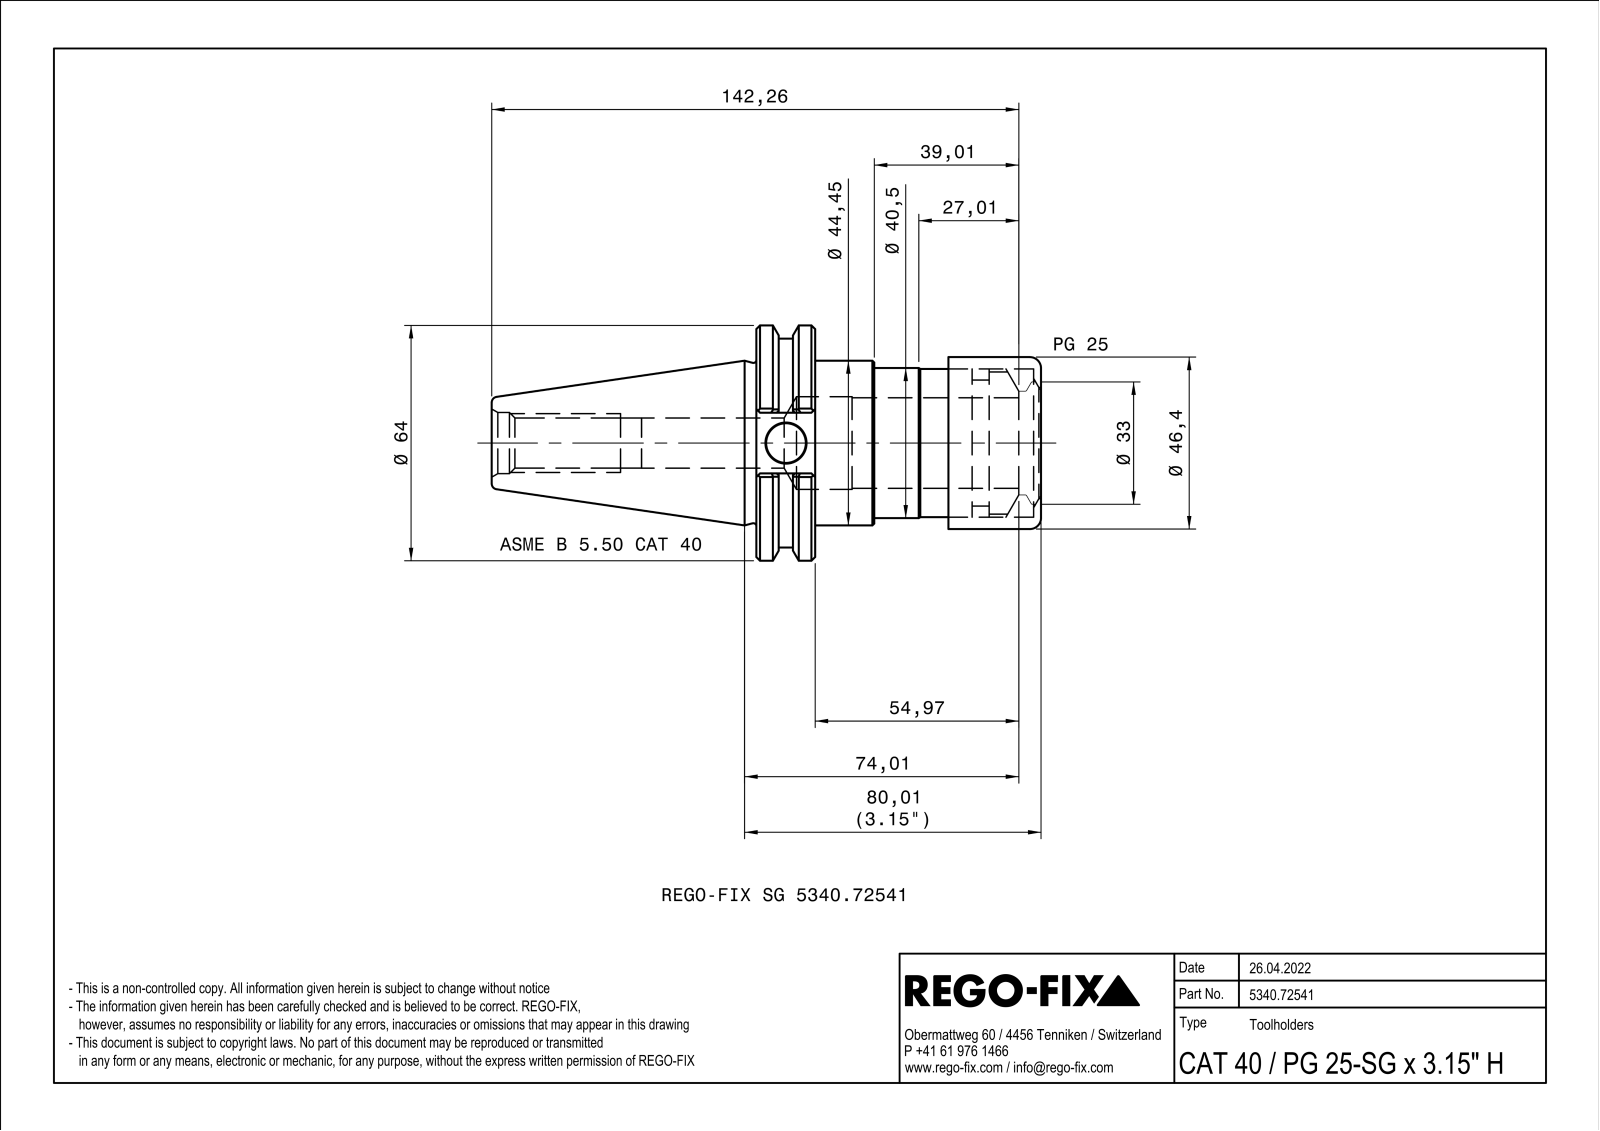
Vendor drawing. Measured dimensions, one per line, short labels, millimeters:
name: NOCUT
written by: SIEMENS PLM Software Solid Edge ST10 (AUTOMOTIVE_DESIGN)
unit: mm
bodies: 1 solid, 115 faces (40 planar, 25 cylindrical, 50 other)
size: 148.25 × 63.5 × 60.79
volume: 152 672 mm³; area: 39 044 mm²
holes: 1× ⌀10.7, 1× ⌀13.53, 1× ⌀16.5, 1× ⌀25, 1× ⌀30, 1× ⌀38.38, 1× ⌀40.05, 1× ⌀42
bosses: 1× ⌀63.5, 1× ⌀56.36, 1× ⌀46, 1× ⌀44.45, 1× ⌀40.5, 1× ⌀40, 1× ⌀34
rounds: 4× R0.5, 1× R20.62, 1× R22.38
face distances: 15.87, 60.96, 76.83, 25, 35.96, 51.83, 18.6, 6.4, 42.36, 58.23
